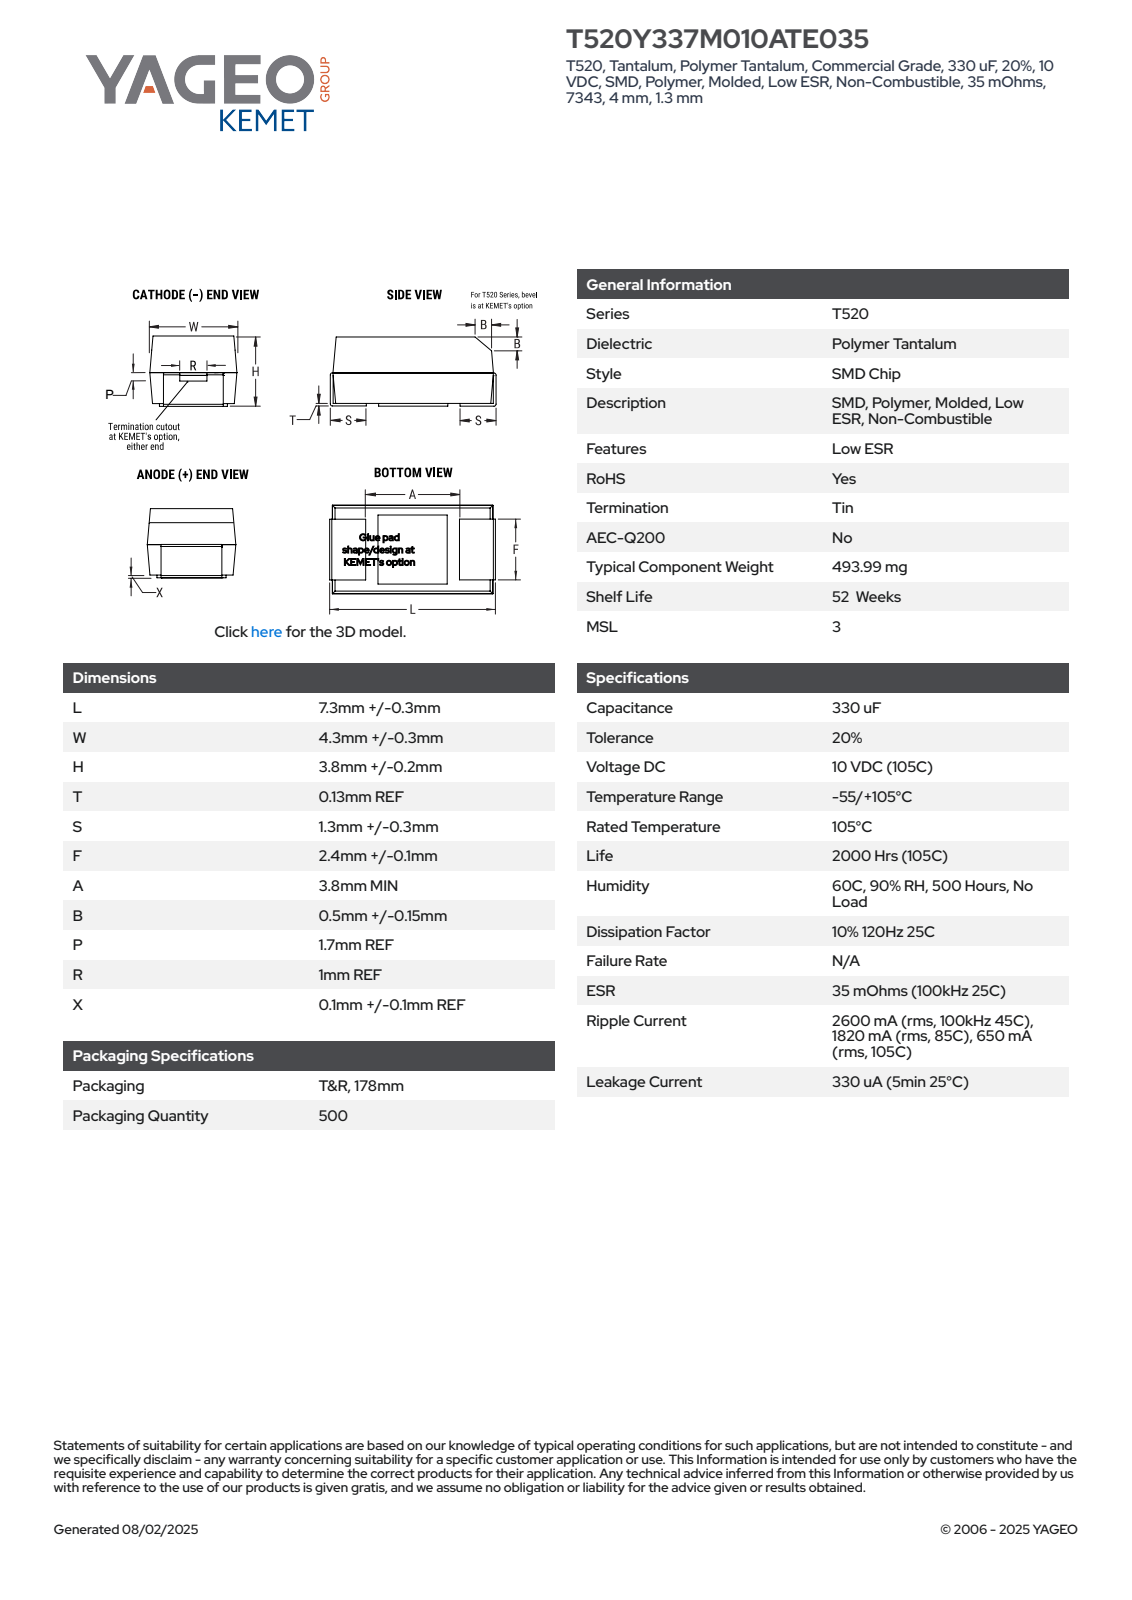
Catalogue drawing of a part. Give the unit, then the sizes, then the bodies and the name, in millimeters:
Units: millimetres
Overall size (bounding box): 7.6 × 4.6 × 4
Main face-to-face distances: 2.02, 1.85, 3.87, 7.31, 1.95, 3.97, 4.59, 4.58, 7.47, 1.98
Volume: 126 mm³ · Surface area: 250 mm²
Bodies: 4 solids, 43 faces (38 planar, 5 cylindrical, 0 other)
Part name (STEP PRODUCT): Case_Anode_31; Case_Bottom_31; Case_Top_31; CTS_7343_L7.60W4.60H4.00S1.3F2.4R1P1.7B0.5 (+1 more)
STEP written by: SolidWorks 2014 (AUTOMOTIVE_DESIGN)
